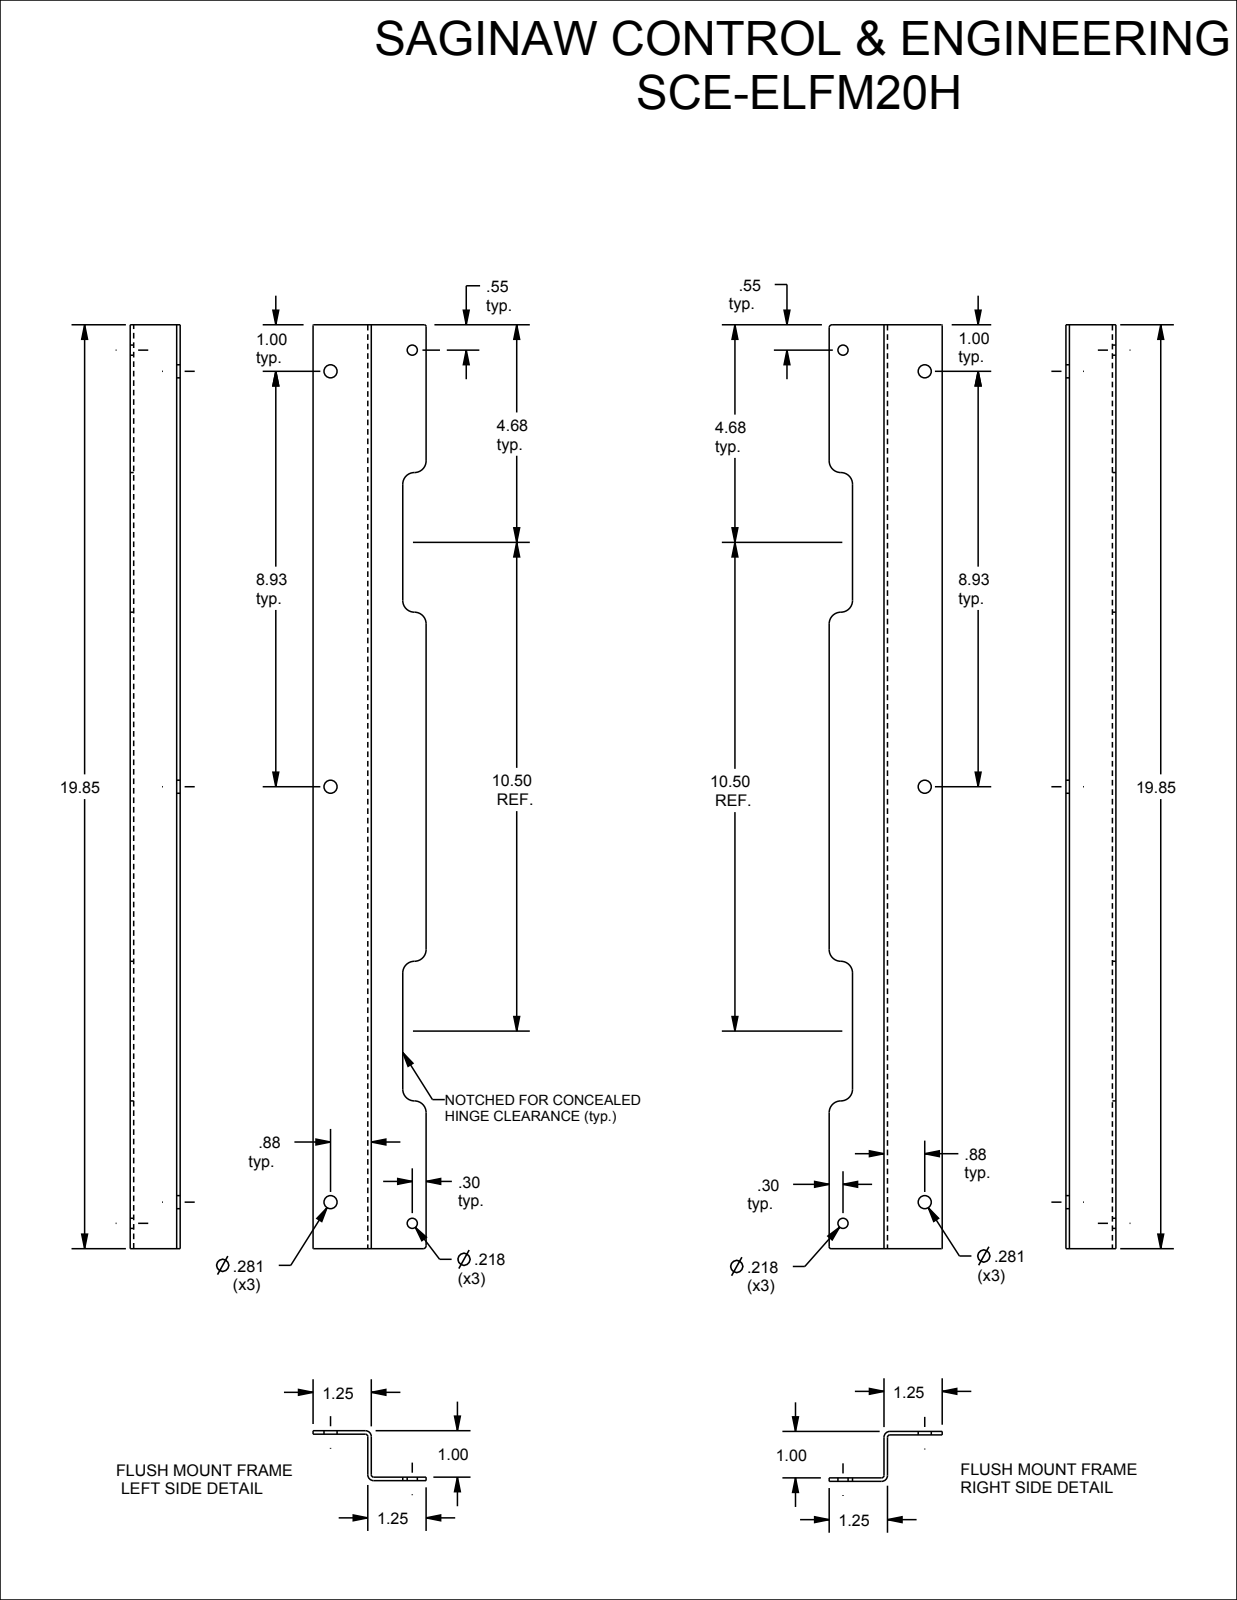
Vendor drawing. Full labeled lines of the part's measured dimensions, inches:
Part name (STEP PRODUCT): SCE-ELFM20H
STEP written by: SolidWorks 2019 (CONFIG_CONTROL_DESIGN)
Units: inches
Bodies: 2 solids, 78 faces (36 planar, 42 cylindrical, 0 other)
Overall size (bounding box): 23 × 19.85 × 1.073
Volume: 9.482 in³ · Surface area: 260.6 in²
Round holes (diameter × count): ⌀0.281 ×6, ⌀0.218 ×4
Partial cylindrical surfaces — rounded edges, fillets, slot ends (radius × count): R0.25 ×16, R0.015 ×4, R0.051 ×4, R0.126 ×4, R0.04 ×2, R0.062 ×2
Main face-to-face distances: 0.075, 0.075, 0.923, 0.998, 0.998, 1.073, 20.575, 20.65, 20.5, 20.575
Hole centre spacings: 1.813, 8.925, 9.543, 18.389, 20.5, 22.539, 23.973, 27.479
